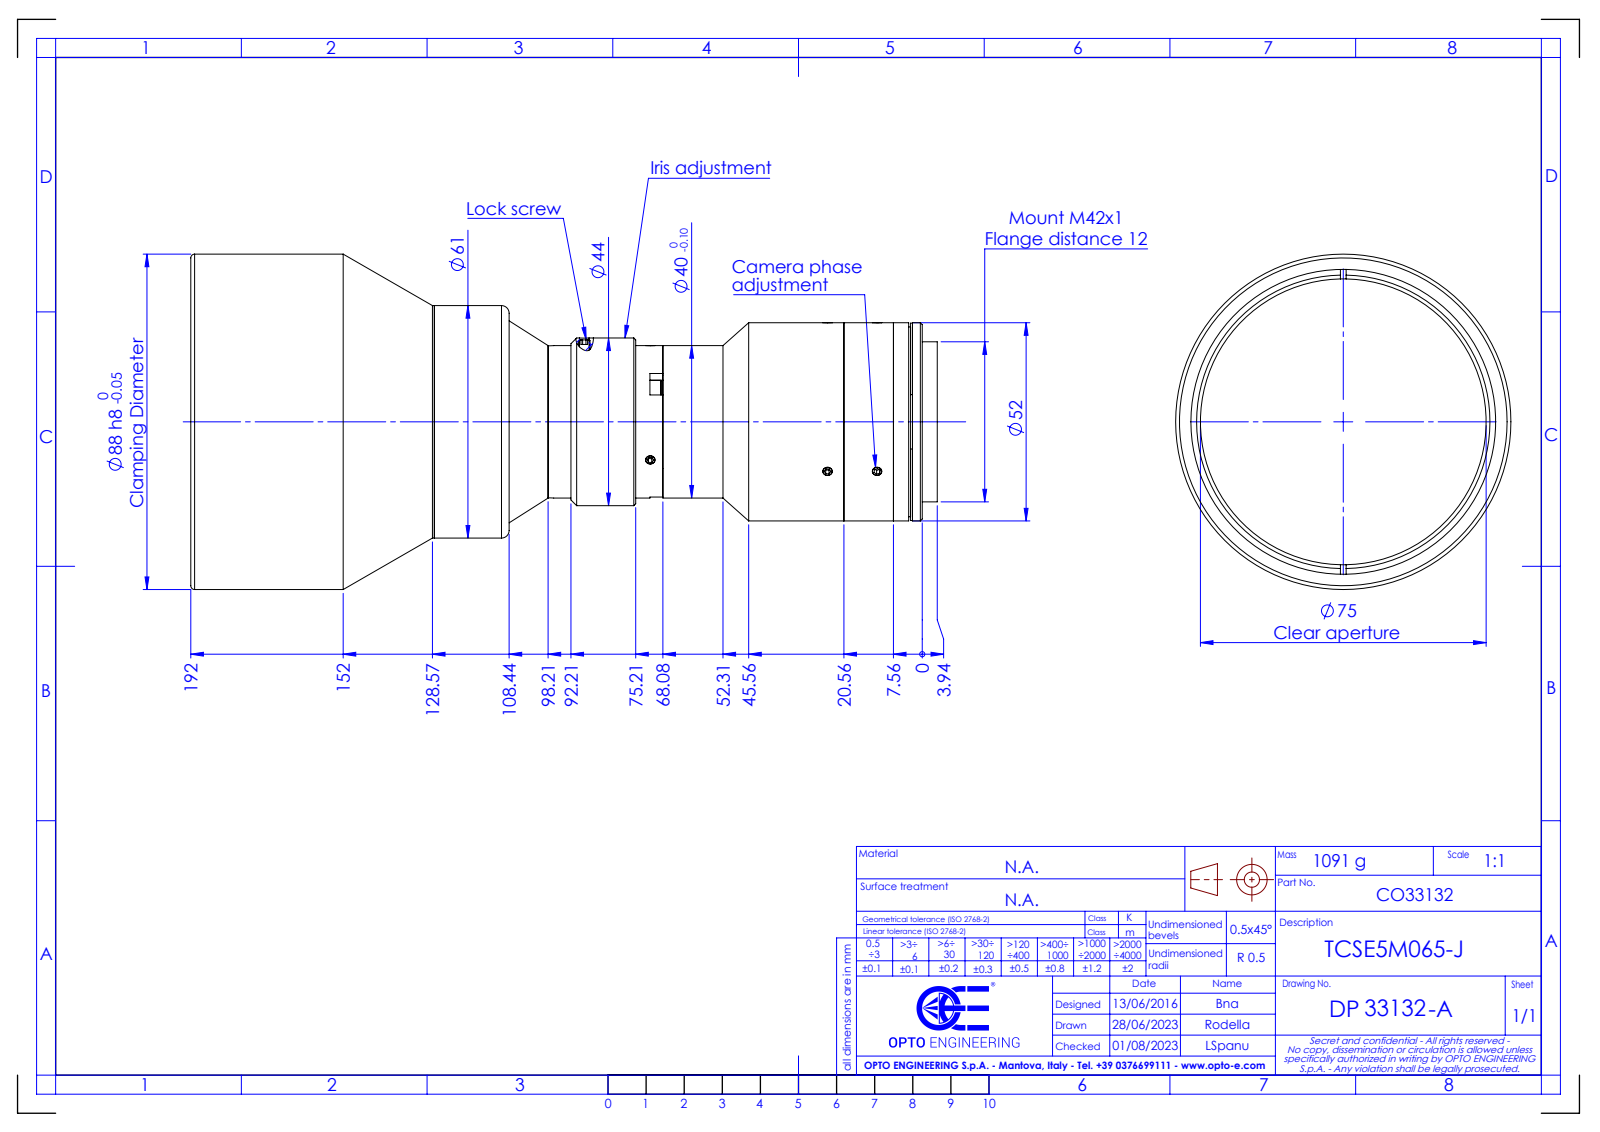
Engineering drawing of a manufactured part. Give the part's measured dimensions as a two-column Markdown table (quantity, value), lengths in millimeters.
| quantity | value |
| --- | --- |
| part name | DP33132-A_TCSE5M065-J |
| STEP written by | SolidWorks 2021 (CONFIG_CONTROL_DESIGN) |
| units | millimeters |
| bodies | 0 solids, 207 faces (105 planar, 55 cylindrical, 47 other) |
| overall size | 195.94 × 88 × 88 |
| round holes (diameter × count) | 2.5 × 1, 37.5 × 1, 38 × 1, 42 × 1, 53 × 1, 75 × 1, 80 × 1 |
| round bosses / shafts (diameter × count) | 5.5 × 3, 88 × 1, 61 × 1, 52 × 1, 51.8 × 1, 44 × 1, 40 × 1, 38.8 × 1 |
| partial cylindrical surfaces (radius × count) | 3.25 × 2, 1.5 × 1 |
| main face-to-face distances | 0.5, 65.02, 65.52, 64.52, 1, 2.56, 68.08, 3.56, 3.06, 123.92 |
